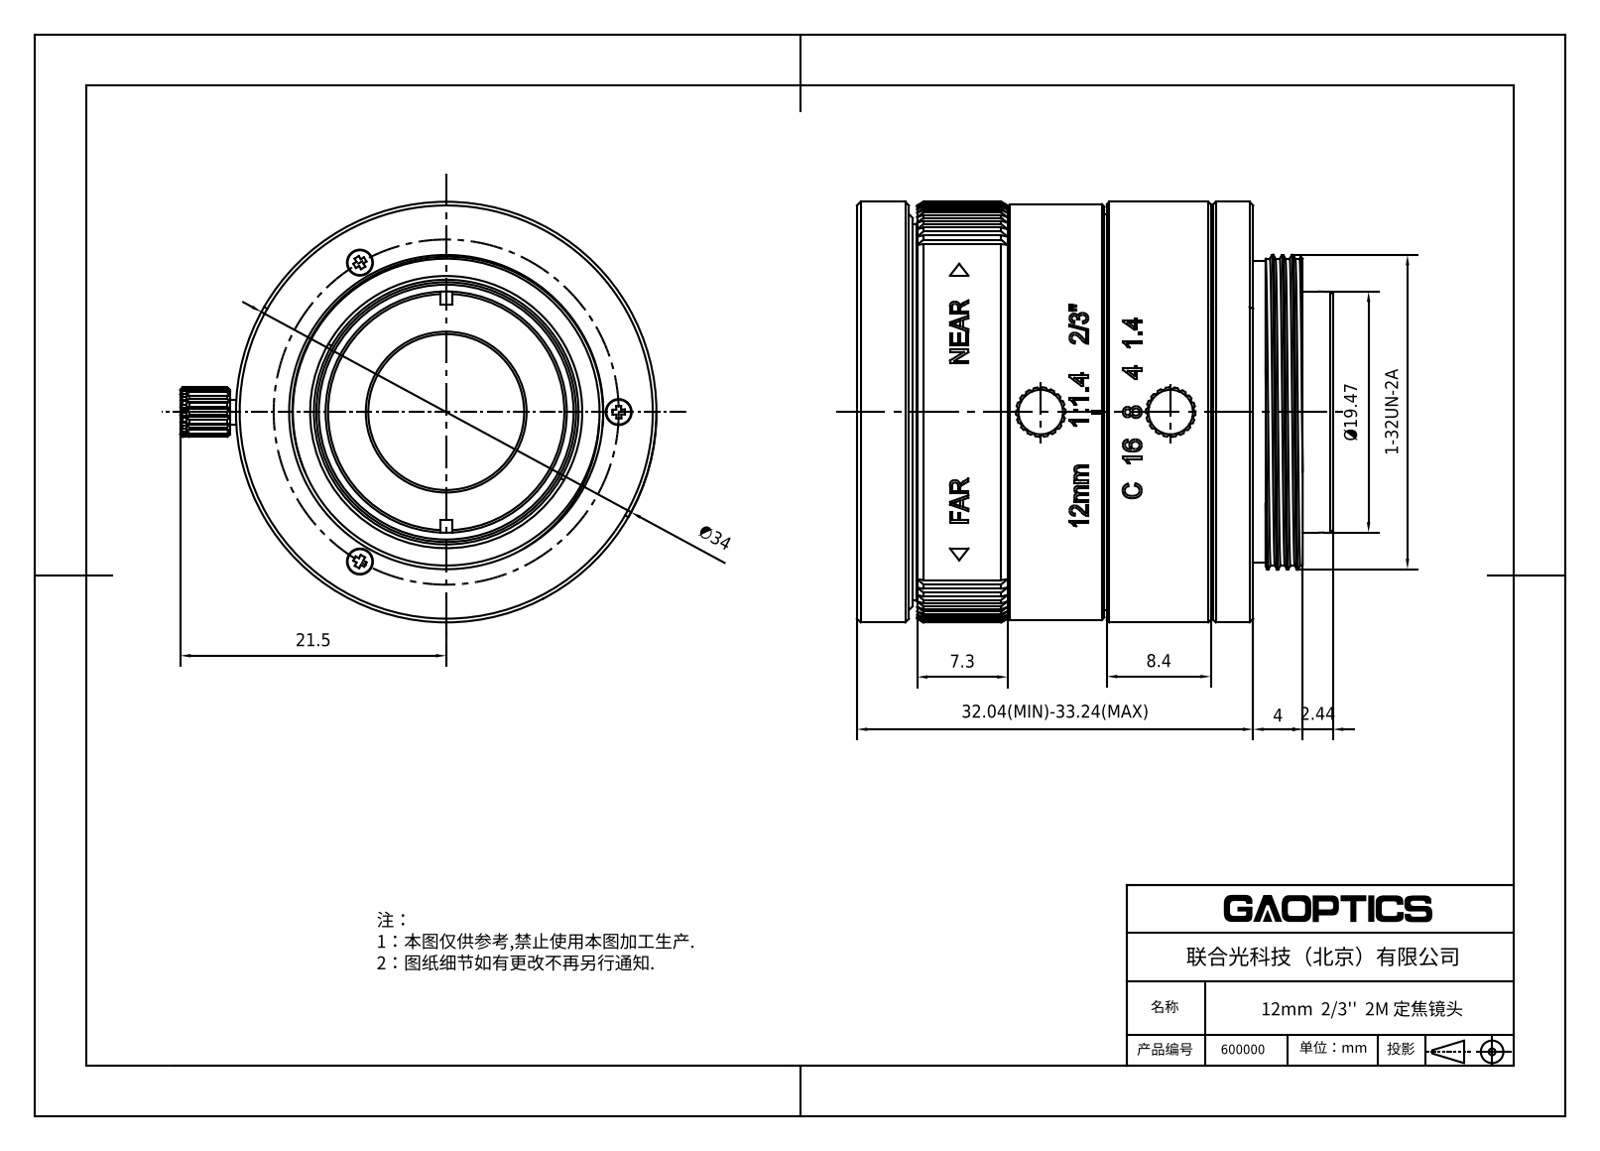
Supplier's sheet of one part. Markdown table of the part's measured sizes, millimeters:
| quantity | value |
| --- | --- |
| part name | 600000 |
| STEP written by | SolidWorks 2020 (CONFIG_CONTROL_DESIGN) |
| units | millimeters |
| bodies | 5 solids, 1447 faces (560 planar, 372 cylindrical, 515 other) |
| overall size | 38.3 × 37.46 × 34 |
| volume | 26 914 mm³ |
| surface area | 12 638 mm² |
| round holes (diameter × count) | 1.4 × 6, 2.1 × 3, 1.2 × 1, 2 × 1, 2.6 × 1, 11.8 × 1, 12.2 × 1, 13.4 × 1, 15.4 × 1, 16.5 × 1, 17.2 × 1, 21.4 × 1 |
| round bosses / shafts (diameter × count) | 2 × 5, 34 × 1, 33.6 × 1, 32 × 1, 31.8 × 1, 30.4 × 1, 29.5 × 1, 28 × 1 |
| partial cylindrical surfaces (radius × count) | 1.25 × 9, 0.5 × 6, 1 × 4, 2 × 2, 16.2 × 1, 16.88 × 1, 16.9 × 1, 17.08 × 1 |
| main face-to-face distances | 3, 28.8, 0.9, 28.45, 0.35, 23.04, 31.45, 31.8, 14.44, 37.46 |
| hole center spacings | 10.5, 13.95, 24.17, 0.56, 9.94, 24.16 |
